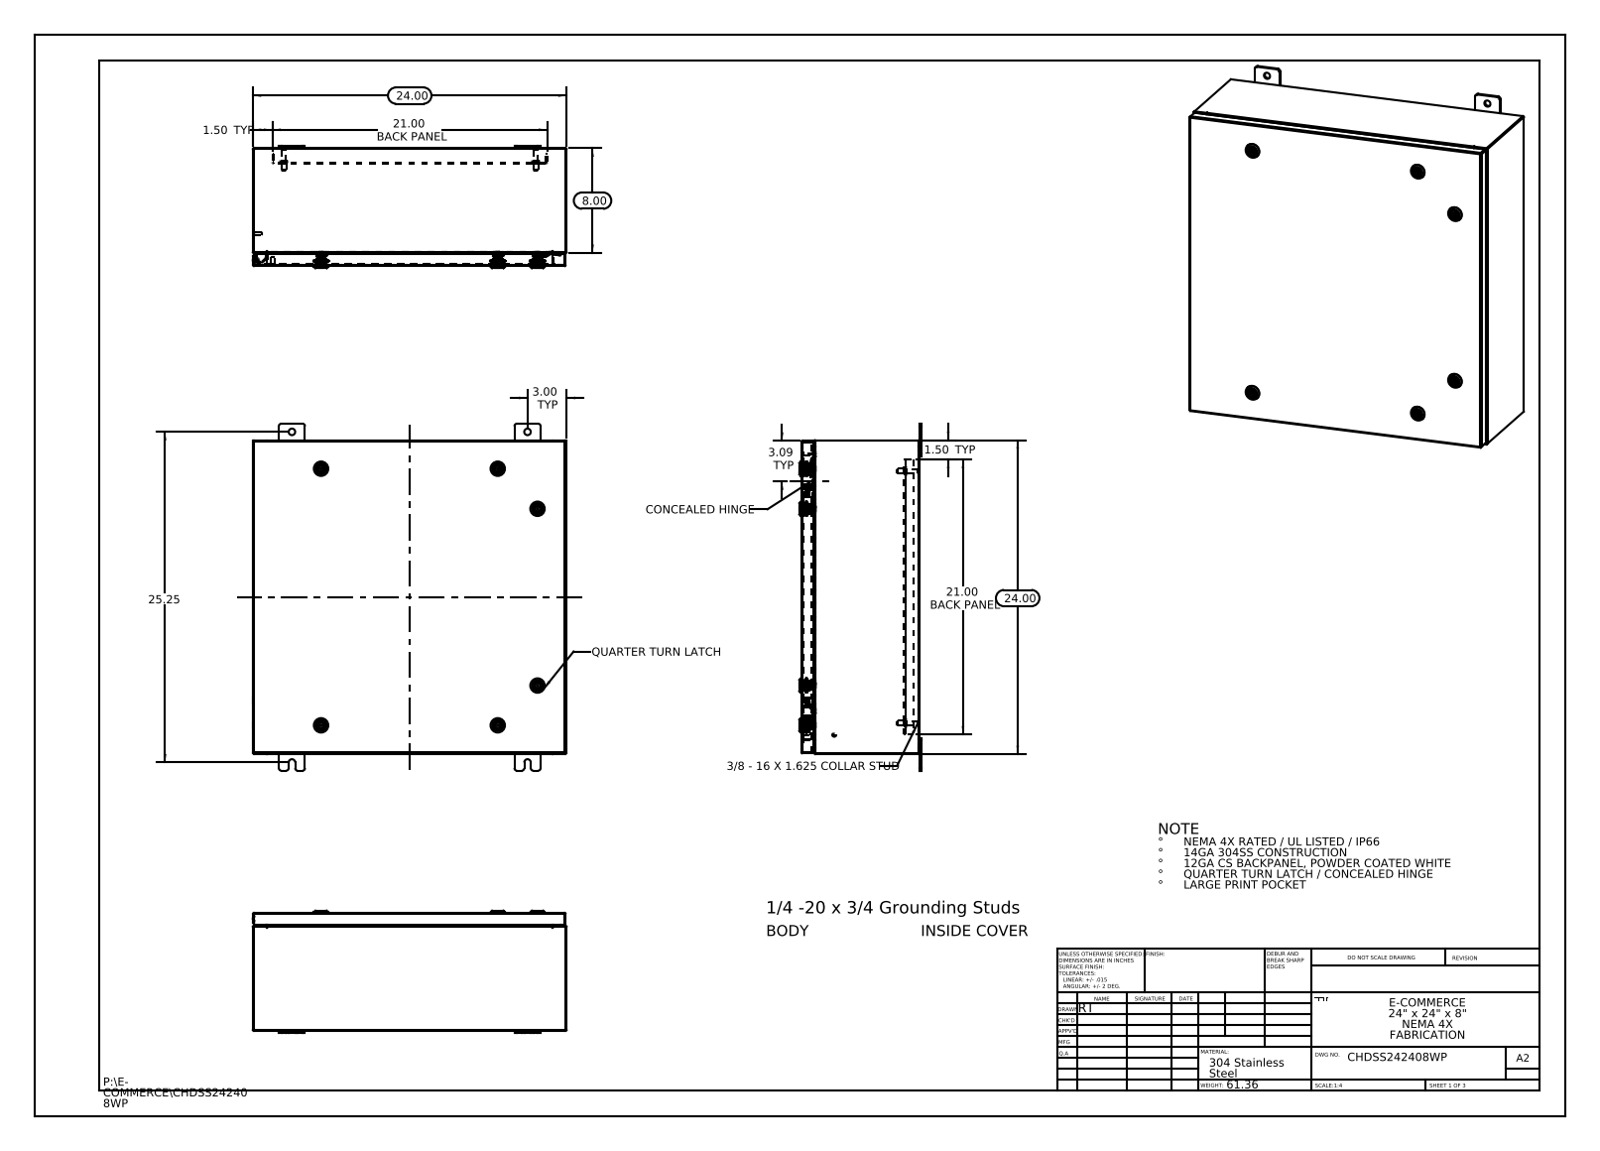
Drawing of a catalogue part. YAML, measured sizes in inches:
part_name: "Concealed Hinge enclosure side; CHDSS242408WP Backpanel; HW-CLH-E5-8004_Cam-232112-U-Industrilas; CHDSS242408WP Cover (+8 more)"
step_written_by: "SolidWorks 2013 (CONFIG_CONTROL_DESIGN)"
units: inches
bodies: {solids: 55, faces: 5420, planar: 1592, cylindrical: 1692, other: 2136}
overall_size: [26.5, 24, 9.356]
volume: 218.6
surface_area: 5453
round_holes:
  - {diameter: 0.5, count: 8}
  - {diameter: 0.197, count: 6}
  - {diameter: 0.394, count: 6}
  - {diameter: 0.4, count: 6}
  - {diameter: 0.63, count: 6}
  - {diameter: 0.787, count: 6}
  - {diameter: 0.136, count: 4}
  - {diameter: 0.211, count: 2}
round_bosses_or_shafts:
  - {diameter: 0.236, count: 8}
  - {diameter: 1.102, count: 6}
  - {diameter: 0.78, count: 6}
  - {diameter: 0.626, count: 6}
  - {diameter: 0.61, count: 6}
  - {diameter: 0.531, count: 6}
  - {diameter: 0.392, count: 6}
  - {diameter: 0.114, count: 6}
partial_cylinders:
  - {radius: 0.006, count: 198}
  - {radius: 0.118, count: 198}
  - {radius: 0.028, count: 72}
  - {radius: 0.02, count: 24}
  - {radius: 0.19, count: 24}
  - {radius: 0.197, count: 24}
  - {radius: 0.013, count: 20}
  - {radius: 0.088, count: 18}
face_to_face_distances: [0.075, 23.925, 0.074, 9.01, 8.935, 8.936, 8.861, 0.104, 1, 1.075]
hole_center_spacings: [13.5, 1.858, 2.878, 3.065, 16.376, 16.815, 18, 19.25]
